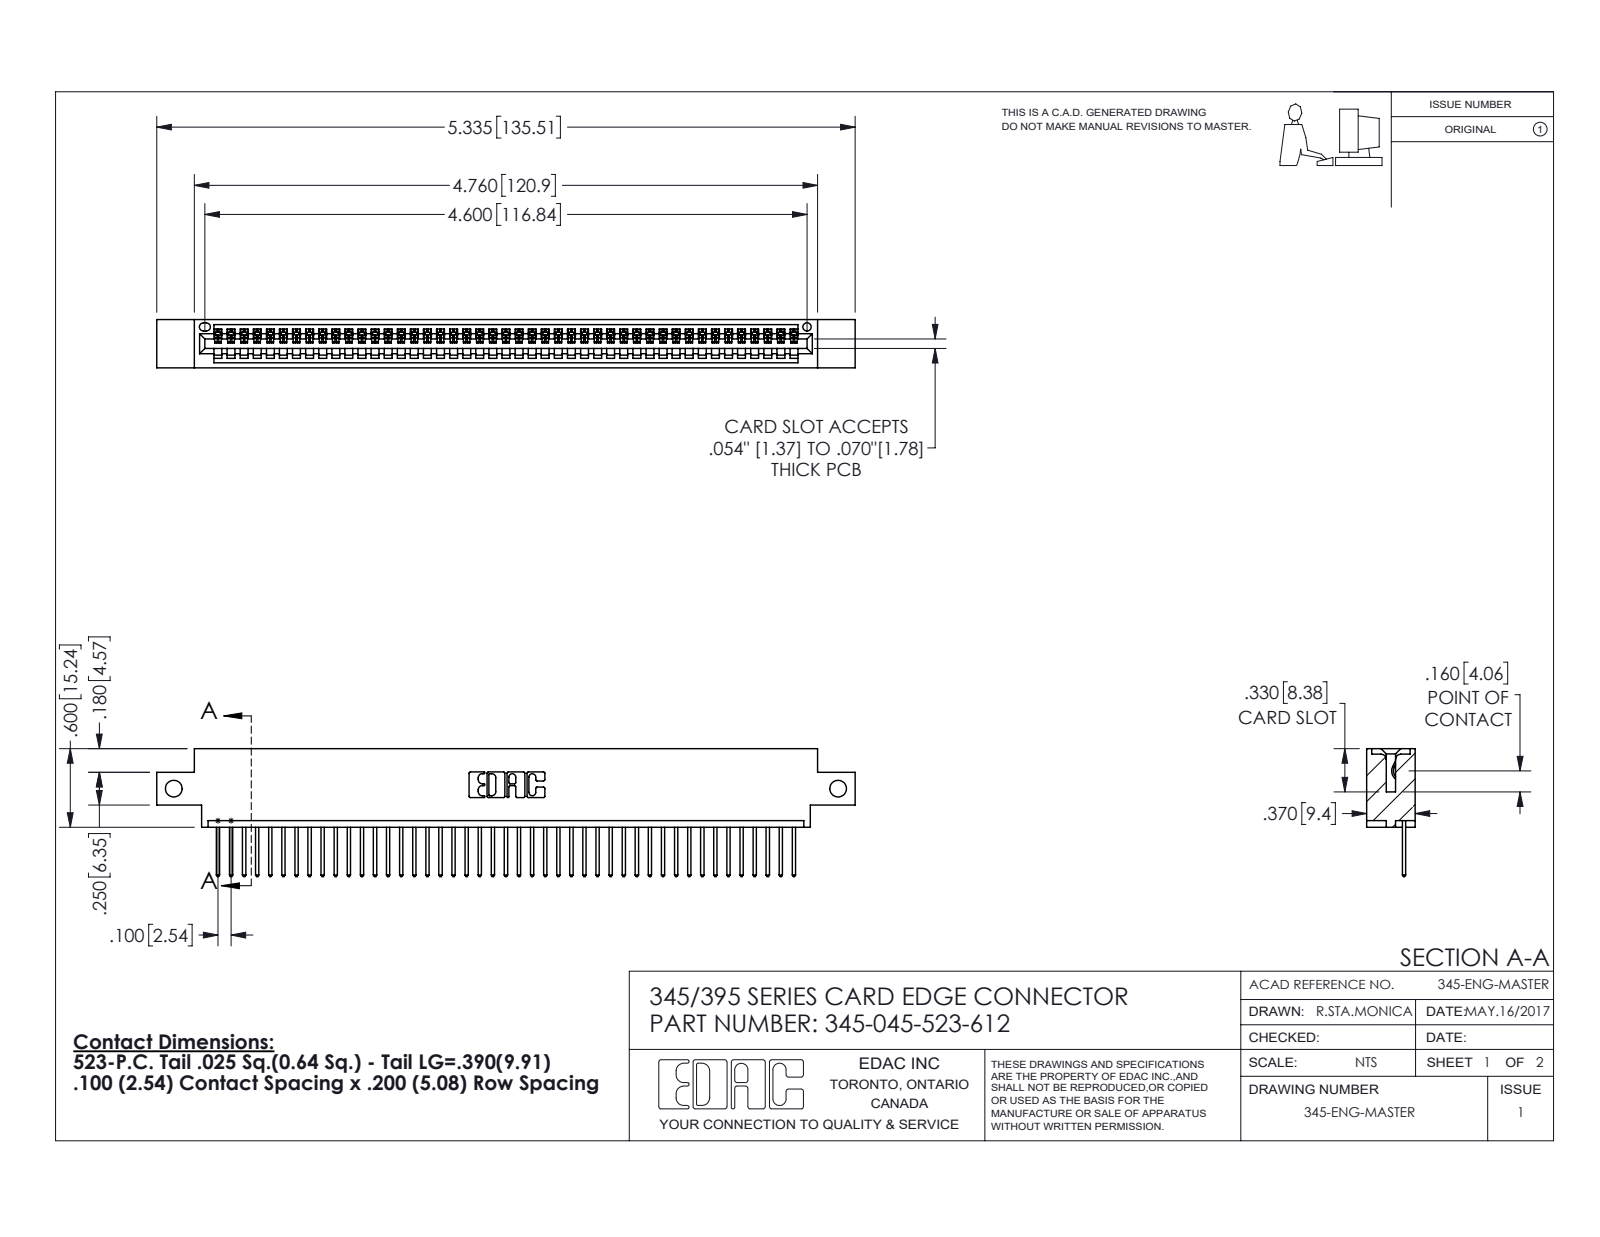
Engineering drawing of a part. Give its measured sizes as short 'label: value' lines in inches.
name: 345-292-001_345-293-123; 345-045-523-612; 345 Part_0.170 Offset - Side Mount
written by: SolidWorks 2016 (CONFIG_CONTROL_DESIGN)
unit: in
bodies: 46 solids, 2740 faces (1884 planar, 856 cylindrical, 0 other)
size: 5.335 × 0.977 × 0.37
volume: 0.774 in³; area: 26.23 in²
holes: 2× ⌀0.128, 1× ⌀0.064
rounds: 90× R0.006, 90× R0.01, 22× R0.01, 6× R0.007, 6× R0.031, 3× R0.026, 2× R0.031, 2× R0.04
face distances: 0.072, 0.298, 0.37, 0.2, 0.098, 0.272, 0.025, 0.225, 0.175, 0.149
hole spacings: 5.075
